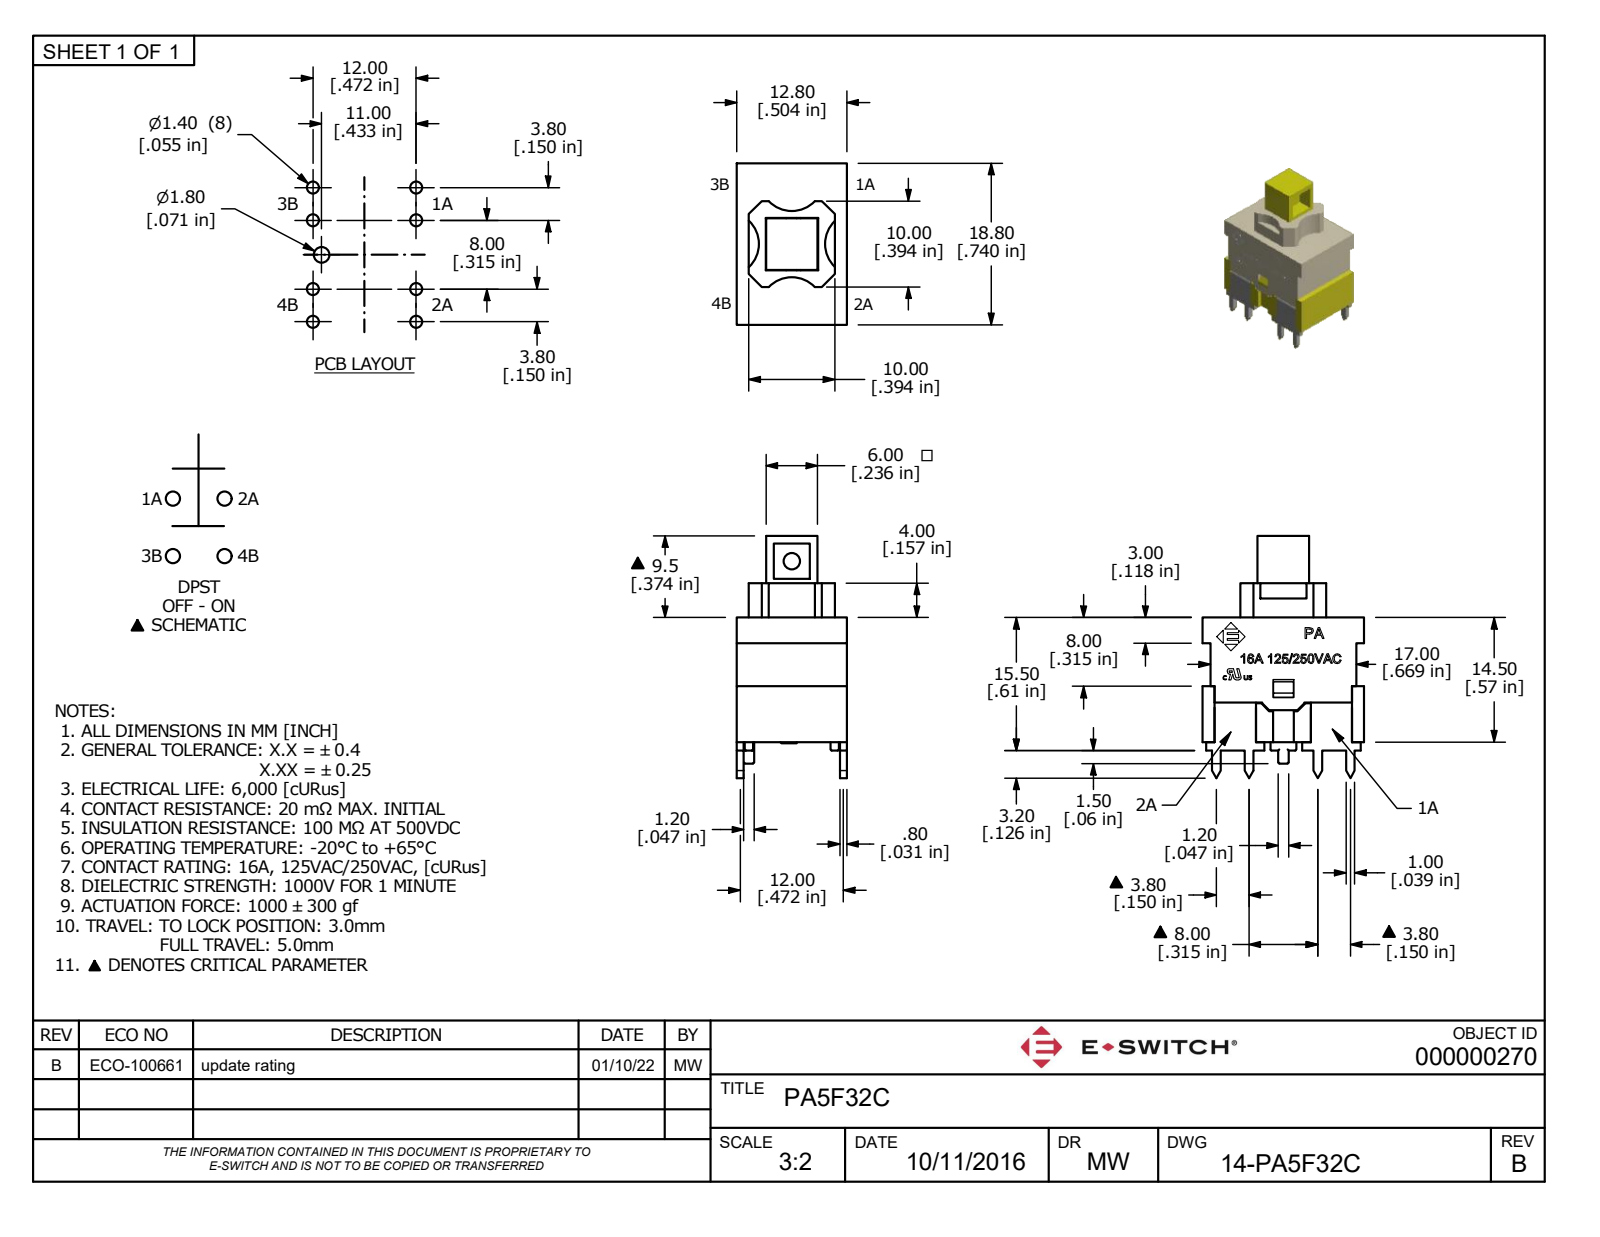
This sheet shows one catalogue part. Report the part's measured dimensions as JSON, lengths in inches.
{"part_name": "PA5F32C", "step_written_by": "Autodesk Inventor 2022 (AUTOMOTIVE_DESIGN)", "units": "inches", "bodies": {"solids": 1, "faces": 851, "planar": 640, "cylindrical": 80, "other": 131}, "overall_size": [1.11, 0.74, 0.504], "volume_in3": 0.131, "surface_area_in2": 6.677, "round_holes": [[0.118, 1]], "round_bosses_or_shafts": [[0.037, 4], [0.098, 2], [0.075, 1]], "partial_cylinders_radius": [[0.01, 26], [0.005, 16], [0.006, 8], [0.039, 4], [0.146, 4], [0.024, 2], [0.07, 2], [0.091, 2]], "face_to_face_distances": [0.031, 0.472, 0.035, 0.661, 0.504, 0.079, 0.217, 0.339, 0.043, 0.173]}
